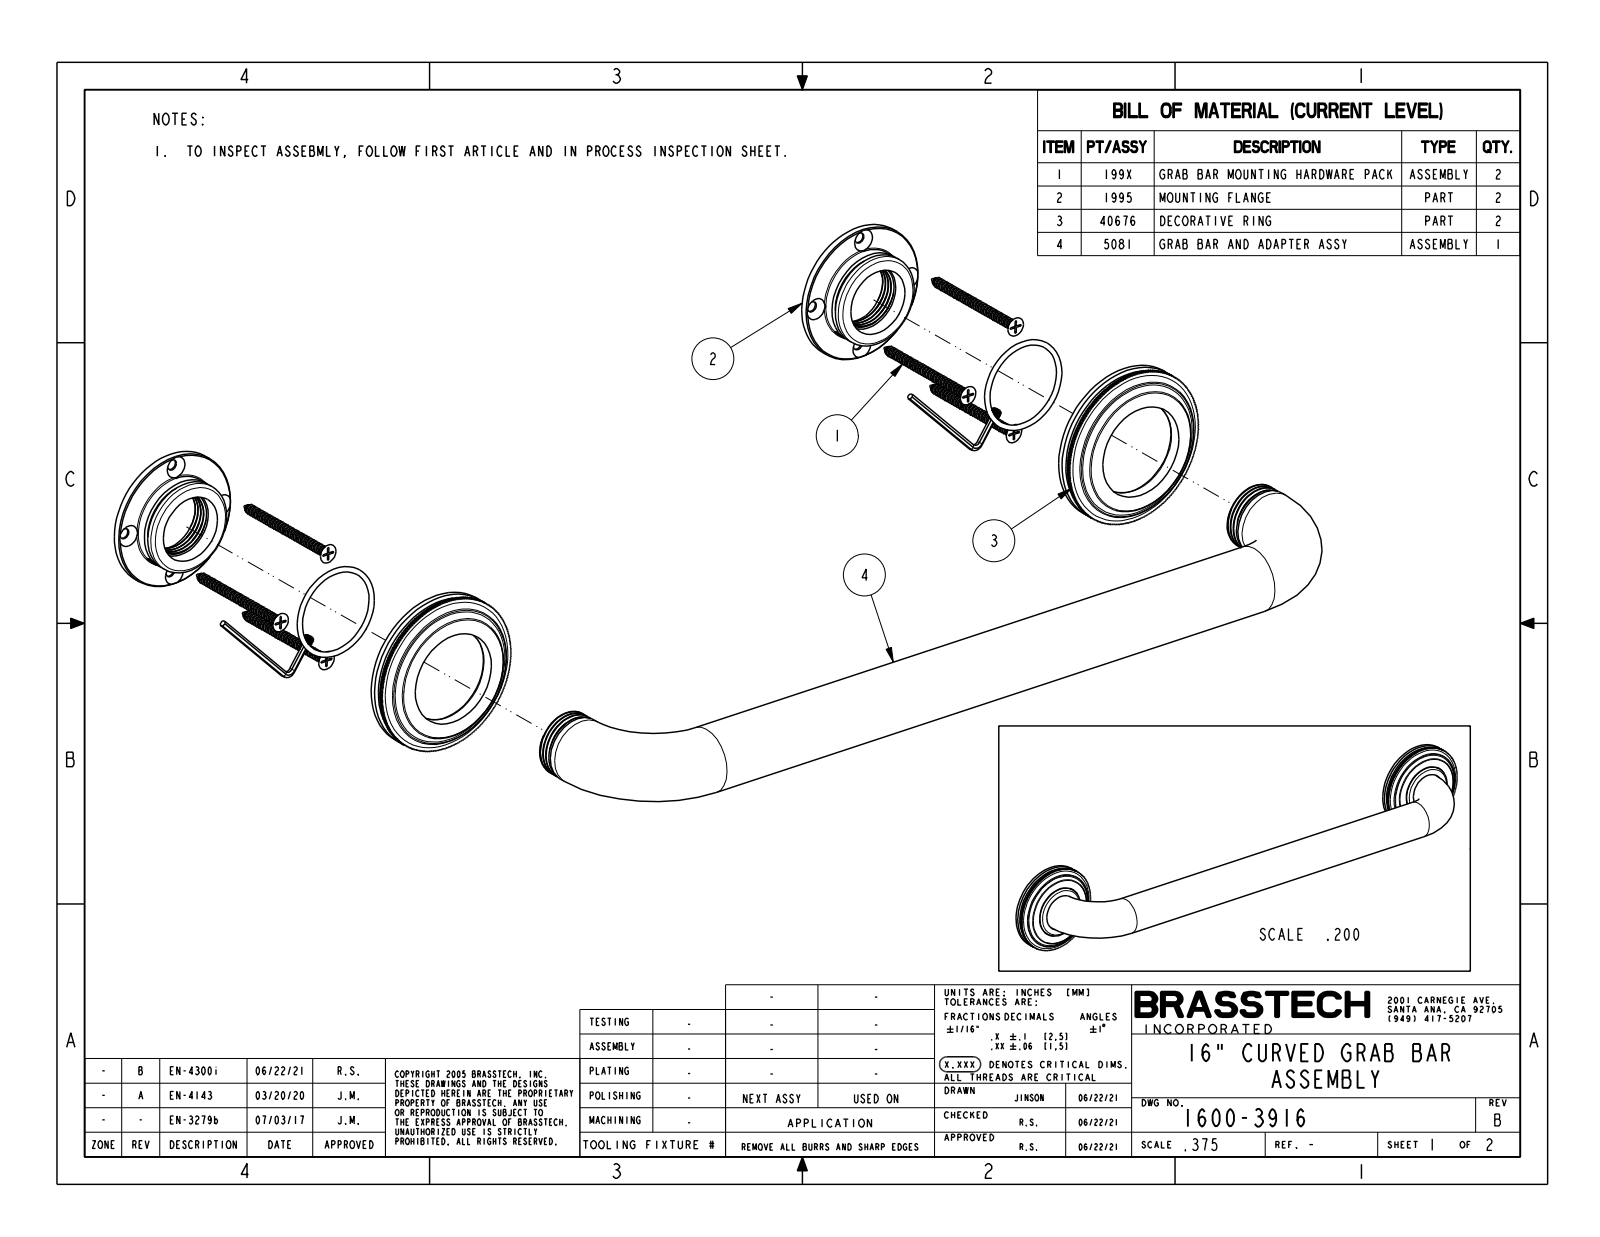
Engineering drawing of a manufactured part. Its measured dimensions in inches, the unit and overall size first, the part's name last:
Units: inches
Overall size (bounding box): 19 × 3 × 2.75
Round bosses / shafts (diameter × count): ⌀3 ×2, ⌀2.9 ×2, ⌀1.75 ×2, ⌀1.25 ×1
Main face-to-face distances: 0.525, 0.6, 0.075, 0.325, 0.2, 0.275, 0.1, 0.25, 0.075, 0.275
Volume: 28.53 in³ · Surface area: 104.8 in²
Bodies: 1 solid, 1134 faces (732 planar, 374 cylindrical, 28 other)
Part name (STEP PRODUCT): 1600-3916_SW0001
STEP written by: CREO PARAMETRIC BY PTC INC, 2018400 (CONFIG_CONTROL_DESIGN)
